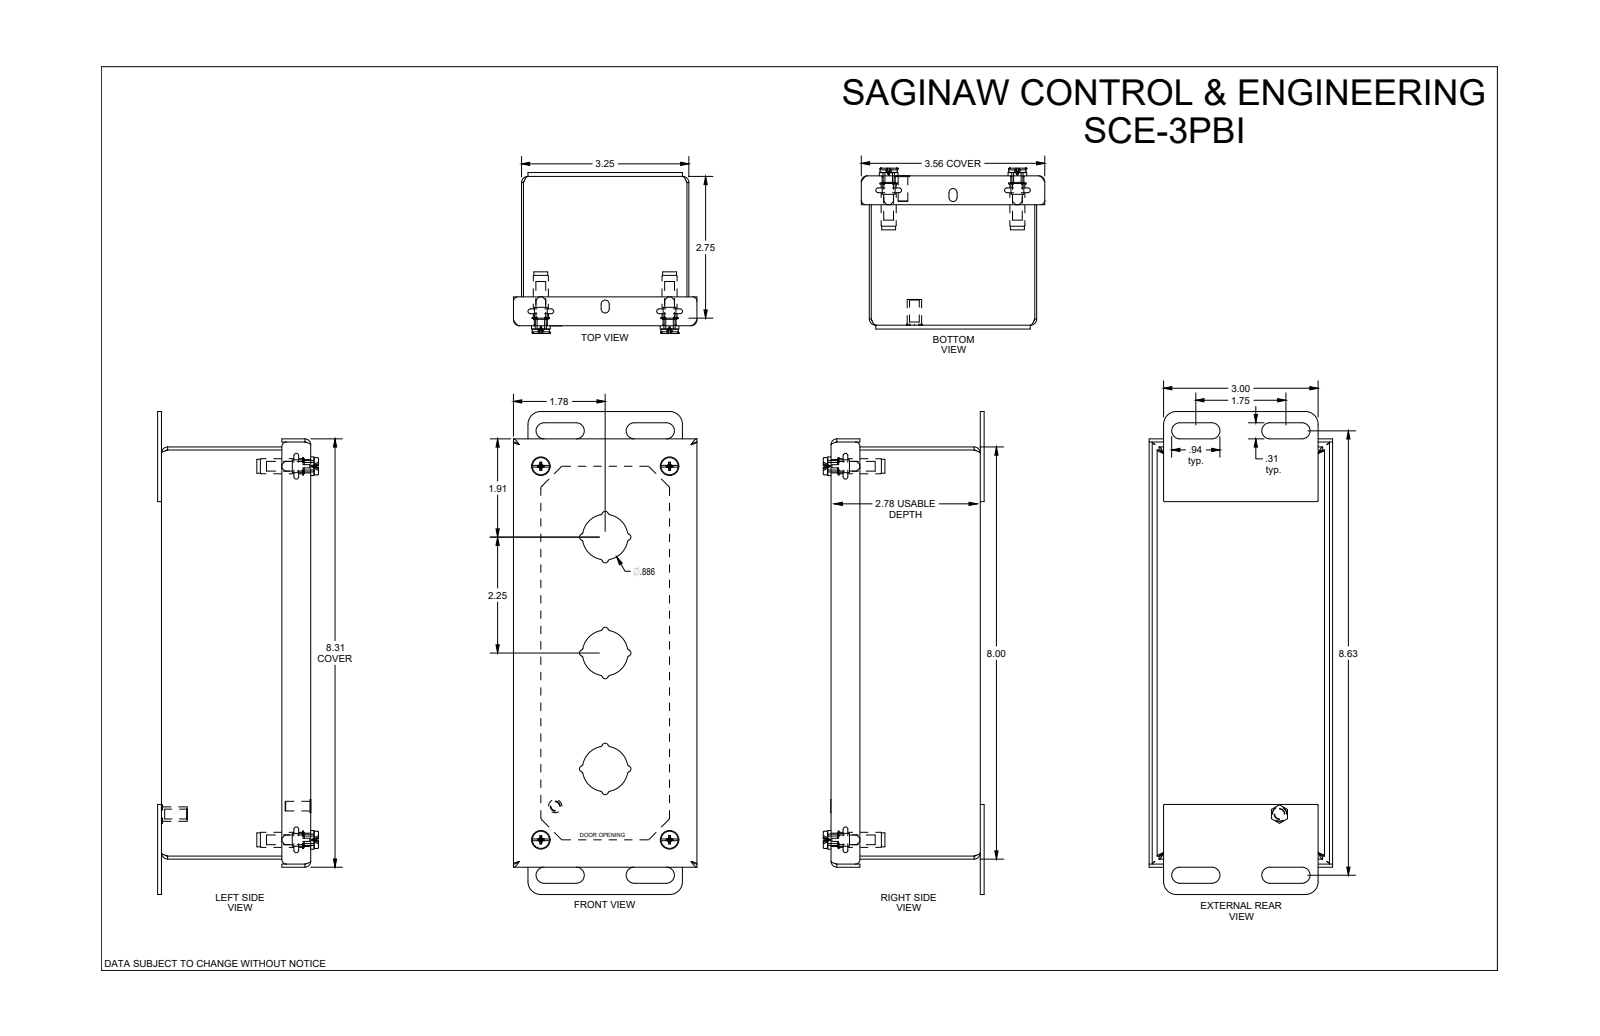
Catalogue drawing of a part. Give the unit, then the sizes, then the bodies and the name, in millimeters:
Units: millimetres
Overall size (bounding box): 238.1 × 90.5 × 79.3
Round holes (diameter × count): ⌀5.6 ×4, ⌀6.8 ×4, ⌀8.6 ×4
Round bosses / shafts (diameter × count): ⌀4.8 ×5, ⌀9.2 ×4, ⌀8.5 ×4, ⌀6.6 ×4, ⌀3.7 ×4, ⌀6.5 ×1
Partial cylindrical surfaces — rounded edges, fillets, slot ends (radius × count): R1 ×44, R2.5 ×20, R1.6 ×12, R0.4 ×8, R1.5 ×8, R2.9 ×8, R4 ×8, R6.2 ×8
Main face-to-face distances: 1.5, 72.1, 1.5, 73.6, 70.6, 81, 82.6, 79.5, 81, 68.3
Hole centre spacings: 63.5, 184.2, 194.8
Volume: 148 100 mm³ · Surface area: 193 100 mm²
Bodies: 14 solids, 482 faces (159 planar, 170 cylindrical, 153 other)
Part name (STEP PRODUCT): SCE-3PBI
STEP written by: SolidWorks 2021 (AUTOMOTIVE_DESIGN)
